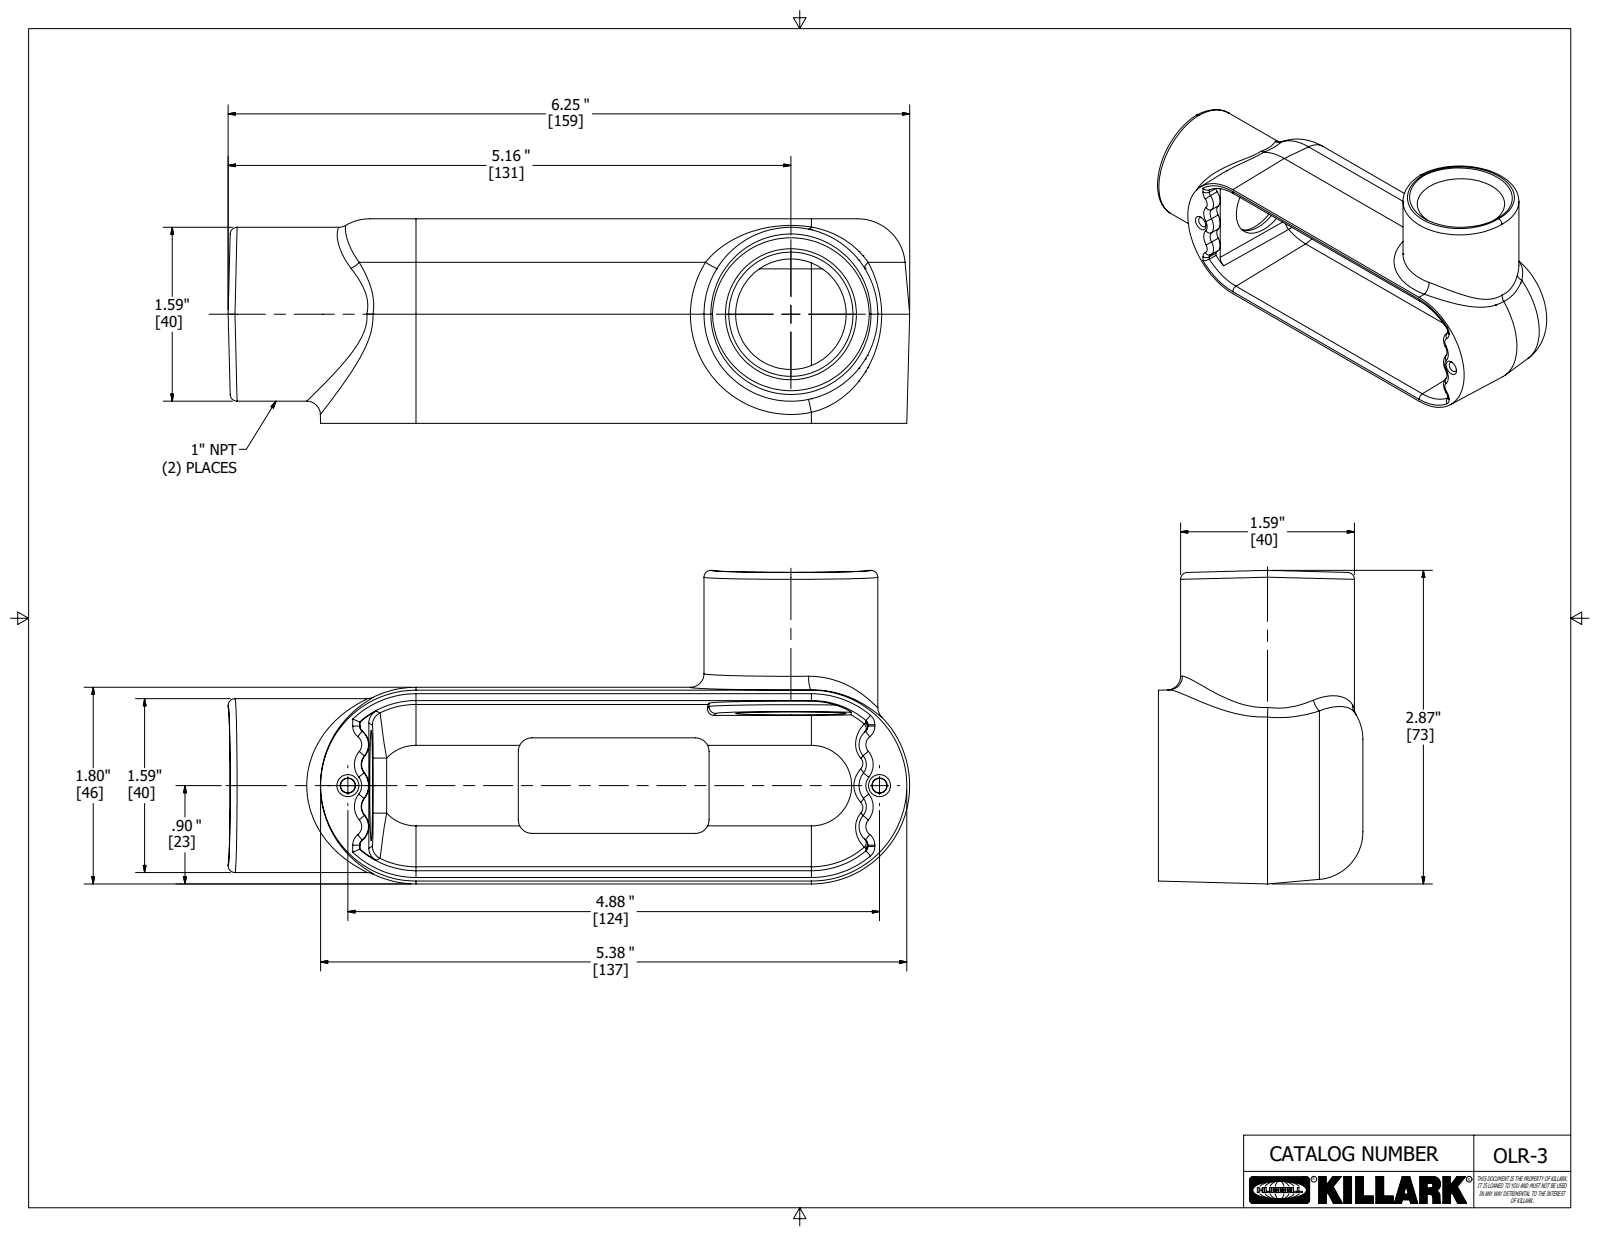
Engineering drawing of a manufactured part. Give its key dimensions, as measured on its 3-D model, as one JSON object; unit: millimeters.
{"part_name": "18135-1b", "step_written_by": "Autodesk Inventor 2018 (AUTOMOTIVE_DESIGN)", "units": "millimeters", "bodies": {"solids": 1, "faces": 150, "planar": 37, "cylindrical": 32, "other": 81}, "overall_size": [158.7, 73, 47.6], "volume_mm3": 93720, "surface_area_mm2": 47490, "round_holes": [[25.7, 2]], "round_bosses_or_shafts": [[40.5, 2]], "partial_cylinders_radius": [[3.2, 11], [1.6, 7], [4, 2], [9.5, 2], [11.1, 2], [4.7, 1], [19.1, 1]], "face_to_face_distances": [42.1, 2.4, 3.2, 0.8, 0.4, 2, 2.8, 47.6, 47.2, 45.2]}
